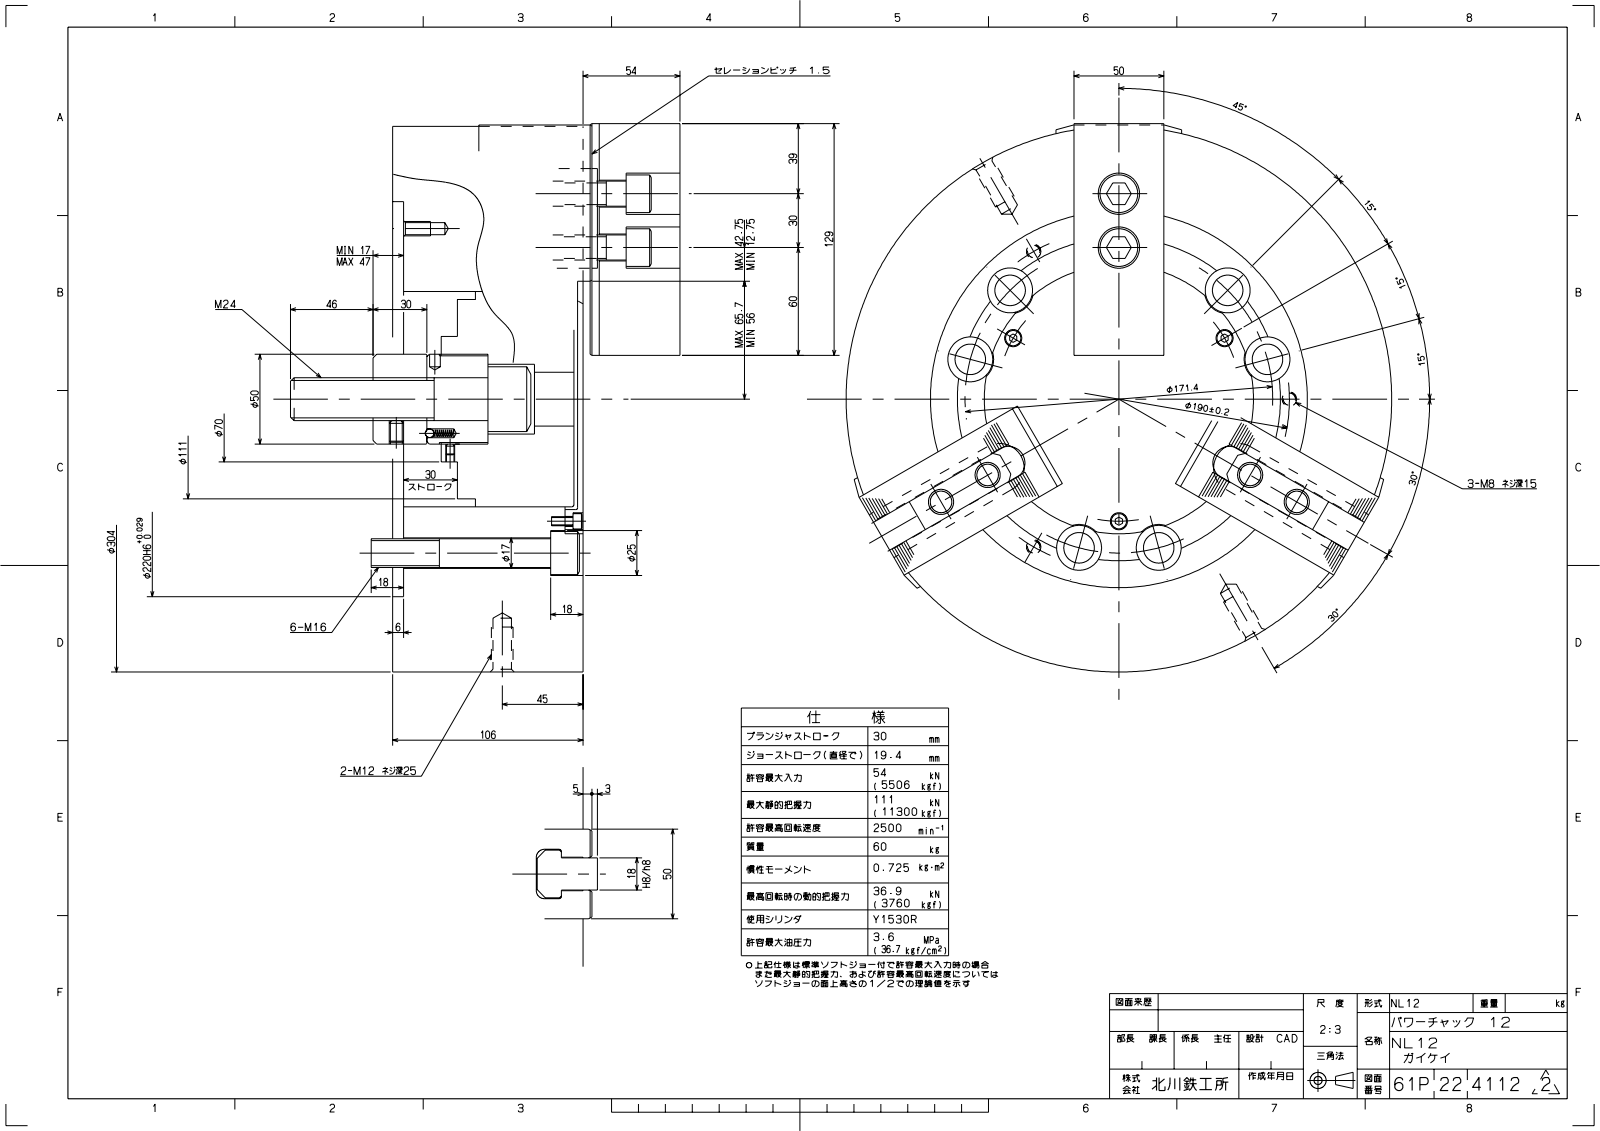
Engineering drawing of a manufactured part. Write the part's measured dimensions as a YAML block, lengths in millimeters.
step_written_by: "ST-DEVELOPER v16.7 (AUTOMOTIVE_DESIGN)"
units: millimeters
bodies: {solids: 1, faces: 3572, planar: 3275, cylindrical: 184, other: 113}
overall_size: [331.75, 329.45, 217.2]
volume: 7734000
surface_area: 640929
round_holes:
  - {diameter: 5, count: 10}
  - {diameter: 14, count: 9}
  - {diameter: 15, count: 9}
  - {diameter: 17, count: 9}
  - {diameter: 25, count: 9}
  - {diameter: 22, count: 6}
  - {diameter: 6, count: 4}
  - {diameter: 8, count: 4}
  - {diameter: 4.2, count: 3}
  - {diameter: 5.5, count: 3}
  - {diameter: 6.8, count: 3}
  - {diameter: 9.5, count: 3}
round_bosses_or_shafts:
  - {diameter: 21, count: 6}
  - {diameter: 24, count: 4}
  - {diameter: 16, count: 3}
  - {diameter: 8.5, count: 3}
  - {diameter: 304, count: 1}
  - {diameter: 120, count: 1}
  - {diameter: 70, count: 1}
  - {diameter: 50, count: 1}
partial_cylinders:
  - {radius: 4.5, count: 6}
  - {radius: 6, count: 6}
  - {radius: 12.5, count: 6}
  - {radius: 13, count: 6}
  - {radius: 9.3, count: 3}
  - {radius: 13.75, count: 3}
  - {radius: 55.5, count: 1}
  - {radius: 60.25, count: 1}
face_to_face_distances: [106, 6, 26, 50, 100, 160.2, 154.2, 54.2, 48, 47.6]
hole_center_spacings: [26.67, 119.91, 122.43, 148.48, 172.11, 199.32, 214.35, 68]
